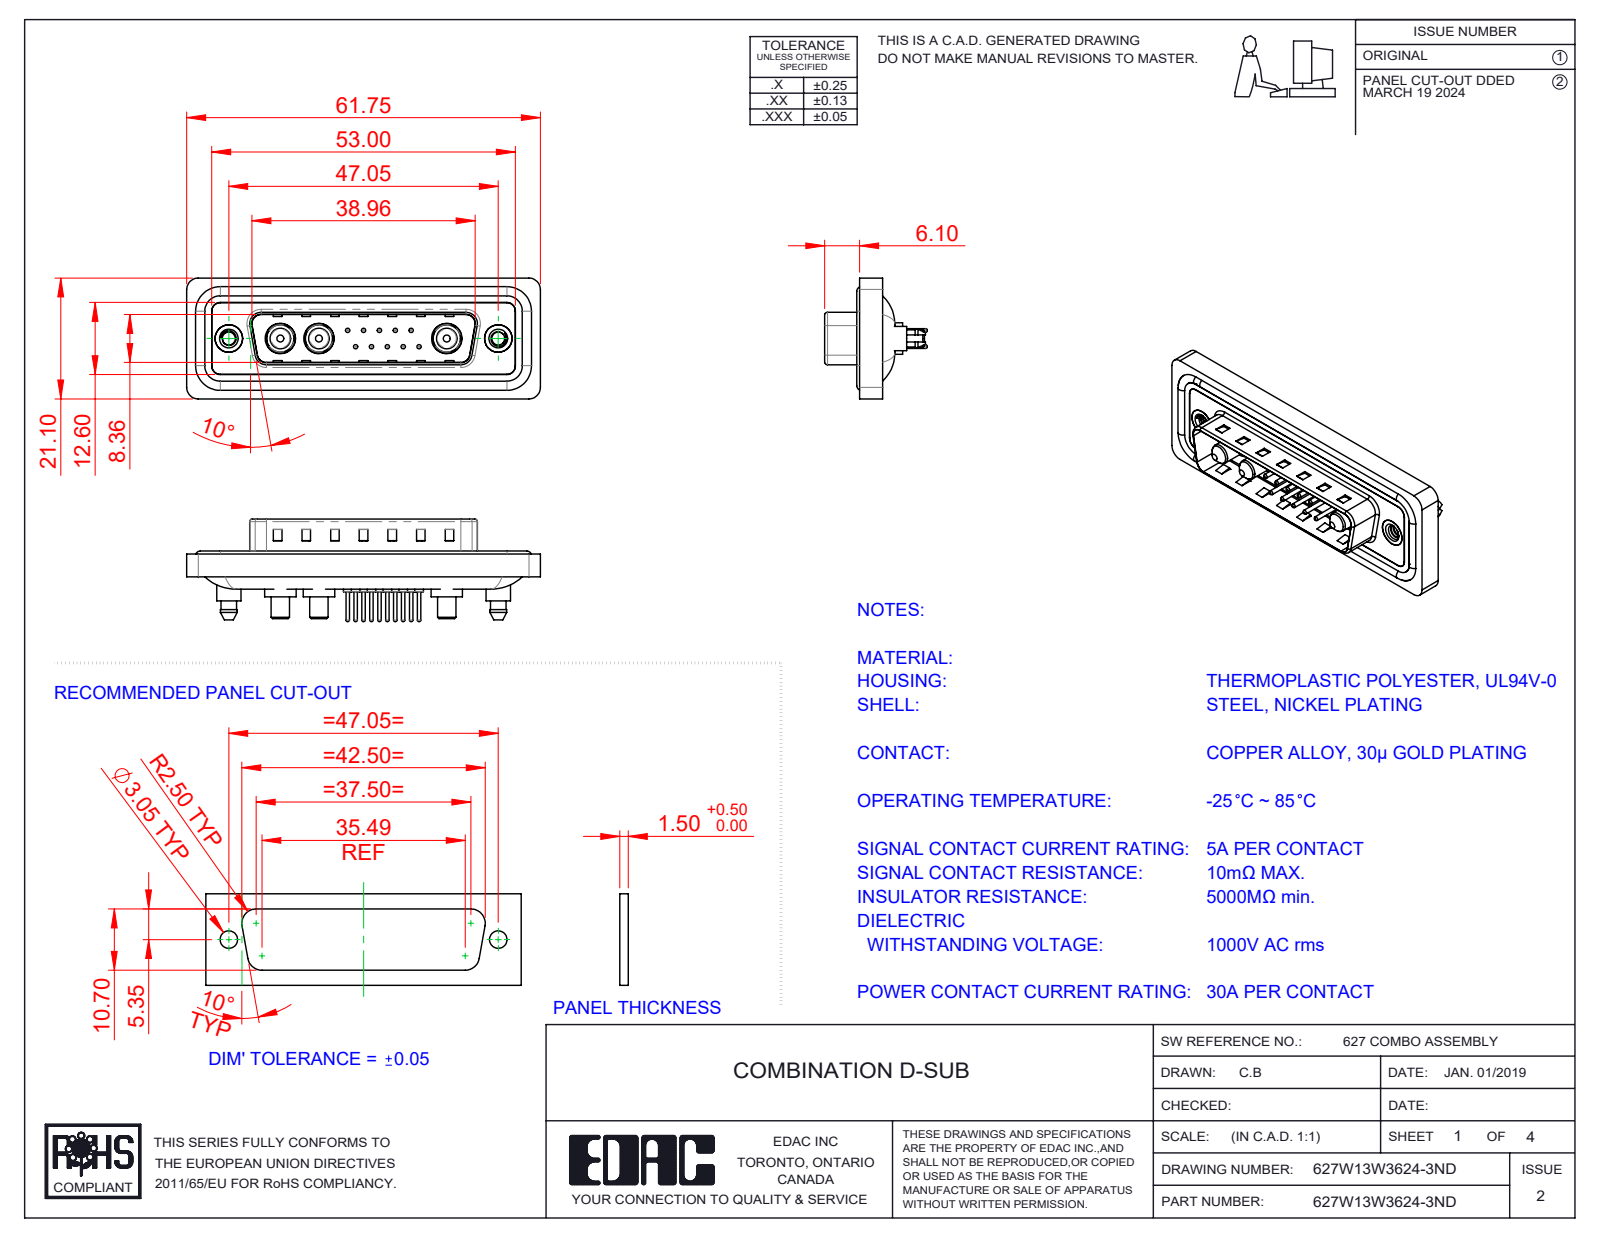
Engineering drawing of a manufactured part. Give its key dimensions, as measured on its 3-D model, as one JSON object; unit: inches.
{"part_name": "627Combo Threaded Boardlock_D; 627Combo Shell Front_25 Contacts; Power Pin_30A S; 627Combo Contact Row 1_24 (+6 more)", "step_written_by": "SolidWorks 2023 (CONFIG_CONTROL_DESIGN)", "units": "inches", "bodies": {"solids": 23, "faces": 1028, "planar": 325, "cylindrical": 425, "other": 278}, "overall_size": [2.431, 0.831, 0.705], "volume_in3": 0.457, "surface_area_in2": 18.95, "round_holes": [[0.03, 10], [0.063, 10], [0.079, 10], [0.191, 3], [0.209, 3], [0.089, 2], [0.157, 2], [0.189, 2], [0.197, 2]], "round_bosses_or_shafts": [[0.059, 10], [0.024, 10], [0.063, 4], [0.217, 3], [0.205, 3], [0.187, 3], [0.148, 3], [0.142, 3]], "partial_cylinders_radius": [[0.059, 24], [0.079, 18], [0.063, 10], [0.02, 8], [0.01, 4], [0.024, 4], [0.026, 4], [0.035, 4]], "face_to_face_distances": [0.016, 0.059, 0.043, 0.063, 0.02, 0.122, 0.114, 0.032, 0.377, 0.161], "hole_center_spacings": [0.124, 0.109, 0.198, 0.218, 0.295, 0.198, 0.327, 0.398]}
